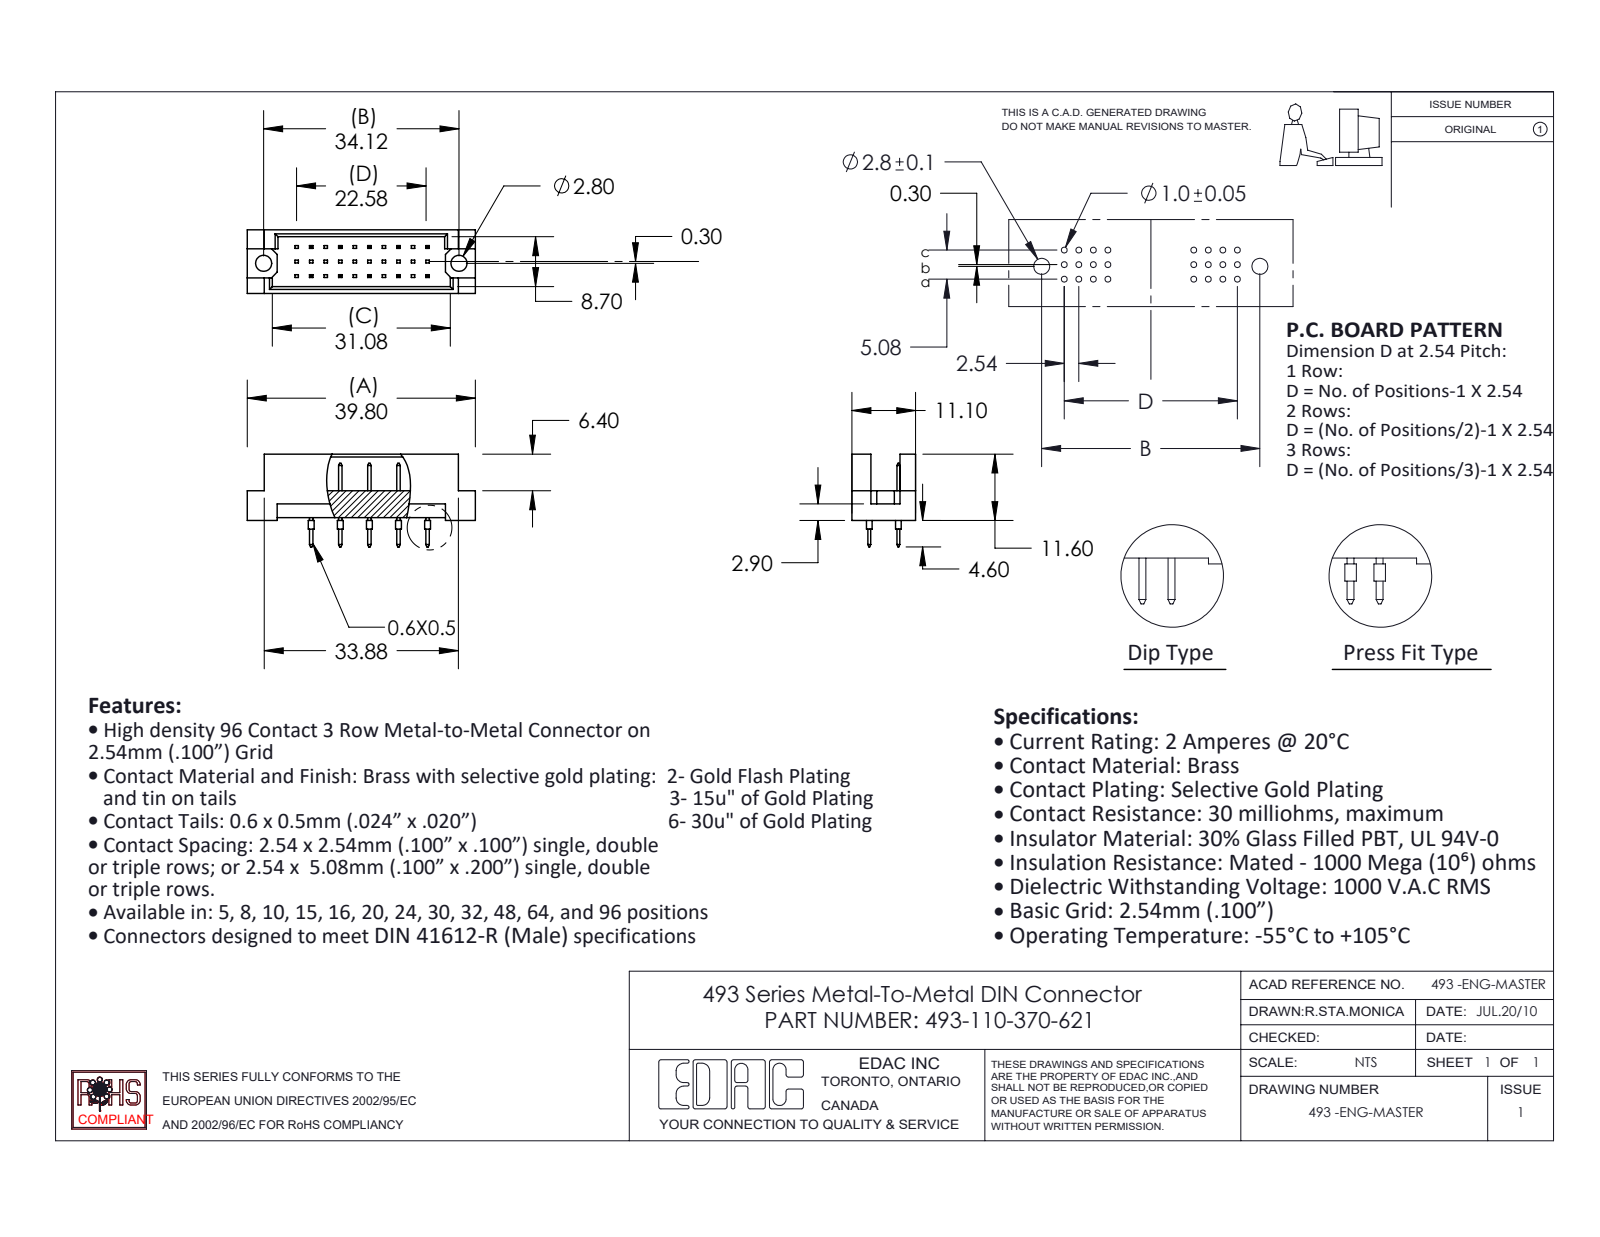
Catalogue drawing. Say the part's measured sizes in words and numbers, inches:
The part is named "493-290_70; 493 Part_30; 493-110-370-621". Its 3-D file was written by "SolidWorks 2020 (CONFIG_CONTROL_DESIGN)". It is 11 solids with 392 faces: 368 planar, 24 cylindrical and 0 other. Overall it measures 1.567 by 0.638 by 0.437 inches. Its volume is 0.148 cubic inches and its surface area 4.772 square inches. Round holes: 2 of diameter 0.11. Round bosses or shafts: 10 of diameter 0.039. The main face-to-face distances are 0.047, 0.39, 0.437, 0.2, 0.343, 0.02, 0.185, 0.094, 0.109, 0.128. The hole center spacings are 1.343.
